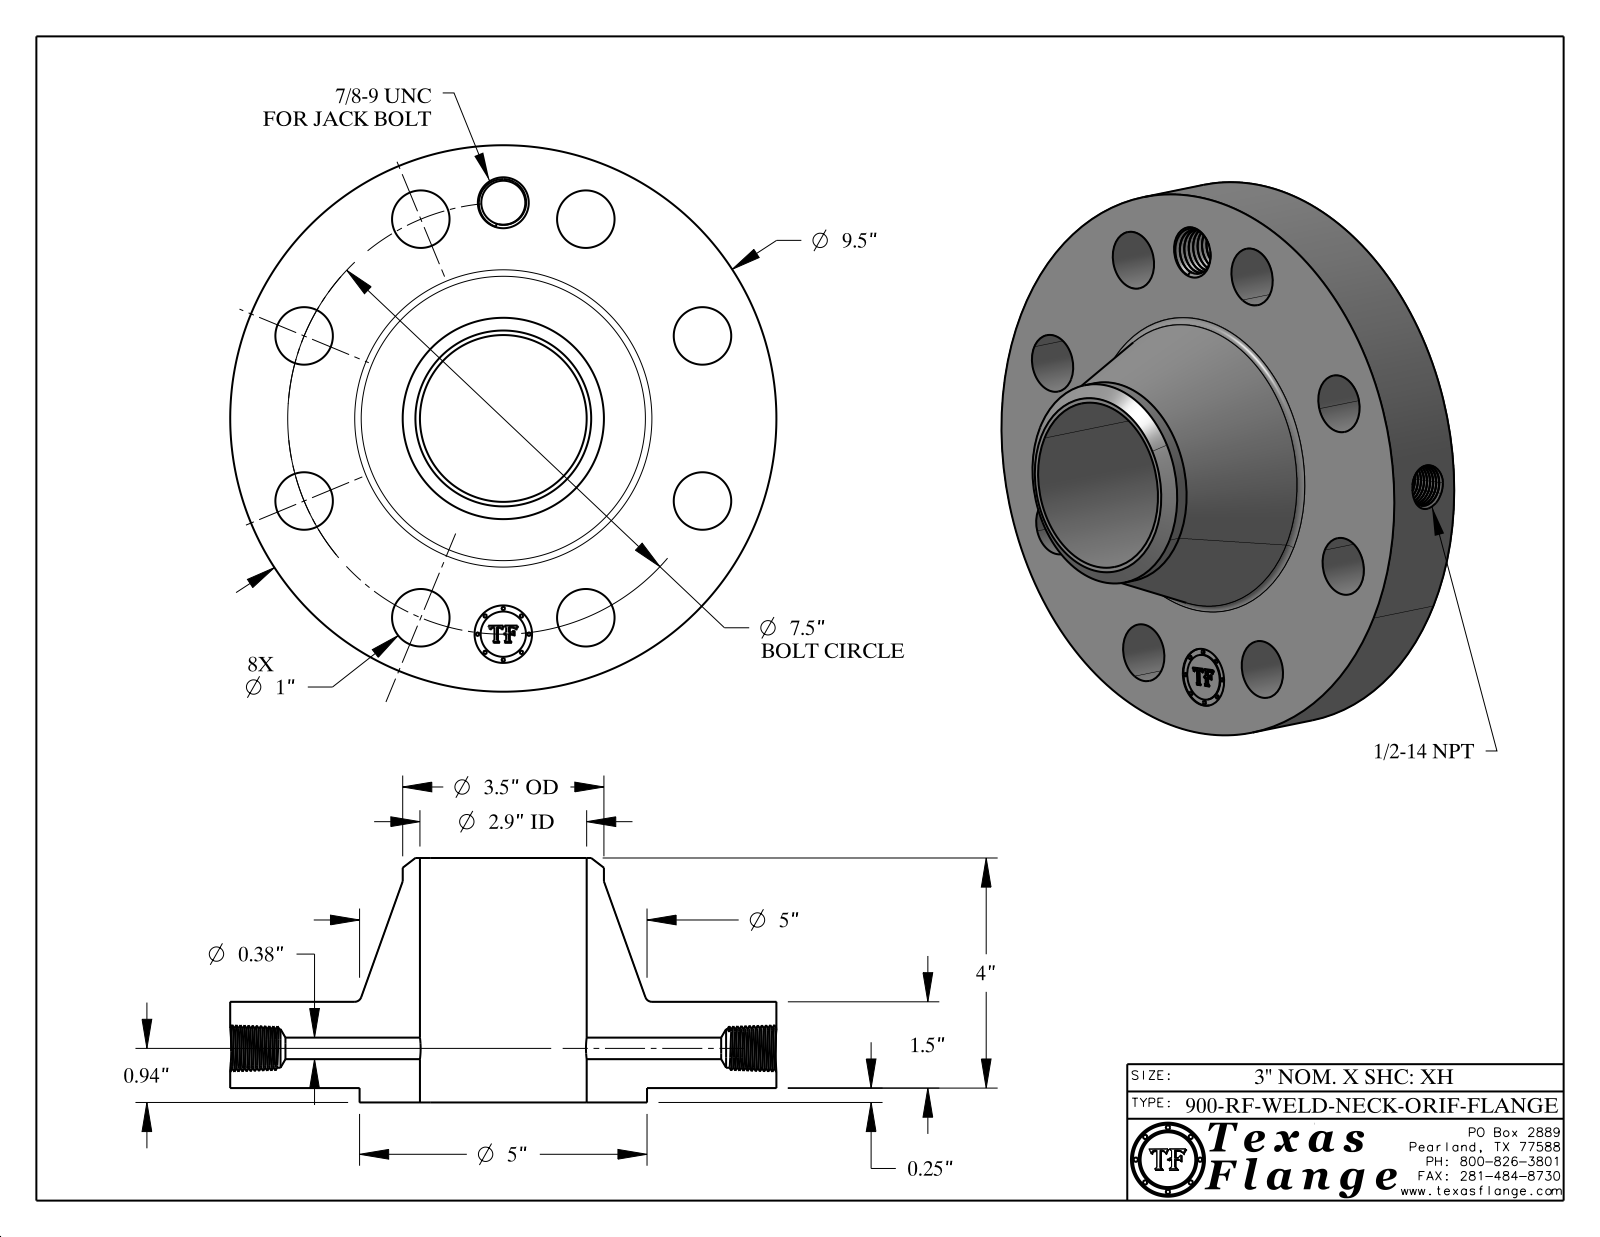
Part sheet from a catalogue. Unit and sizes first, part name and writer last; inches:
Units: inches
Overall size (bounding box): 9.5 × 9.5 × 4.25
Round holes (diameter × count): ⌀1 ×9, ⌀0.375 ×1, ⌀0.672 ×1, ⌀0.766 ×1, ⌀2.9 ×1
Round bosses / shafts (diameter × count): ⌀0.061 ×8, ⌀9.5 ×1, ⌀5 ×1, ⌀3.5 ×1, ⌀0.788 ×1
Main face-to-face distances: 1.5, 0.25, 1.75, 4.25, 4, 2.5, 1.735, 1.485, 0.015, 2.515
Hole centre spacings: 3.75, 2.87, 5.303, 6.929, 7.5, 1.463, 4.167, 6.236
Volume: 105.4 in³ · Surface area: 280.2 in²
Bodies: 1 solid, 759 faces (369 planar, 90 cylindrical, 300 other)
Part name (STEP PRODUCT): 900-RF-WELD-NECK
STEP written by: CATIA V5 STEP AP214 (AUTOMOTIVE_DESIGN)
